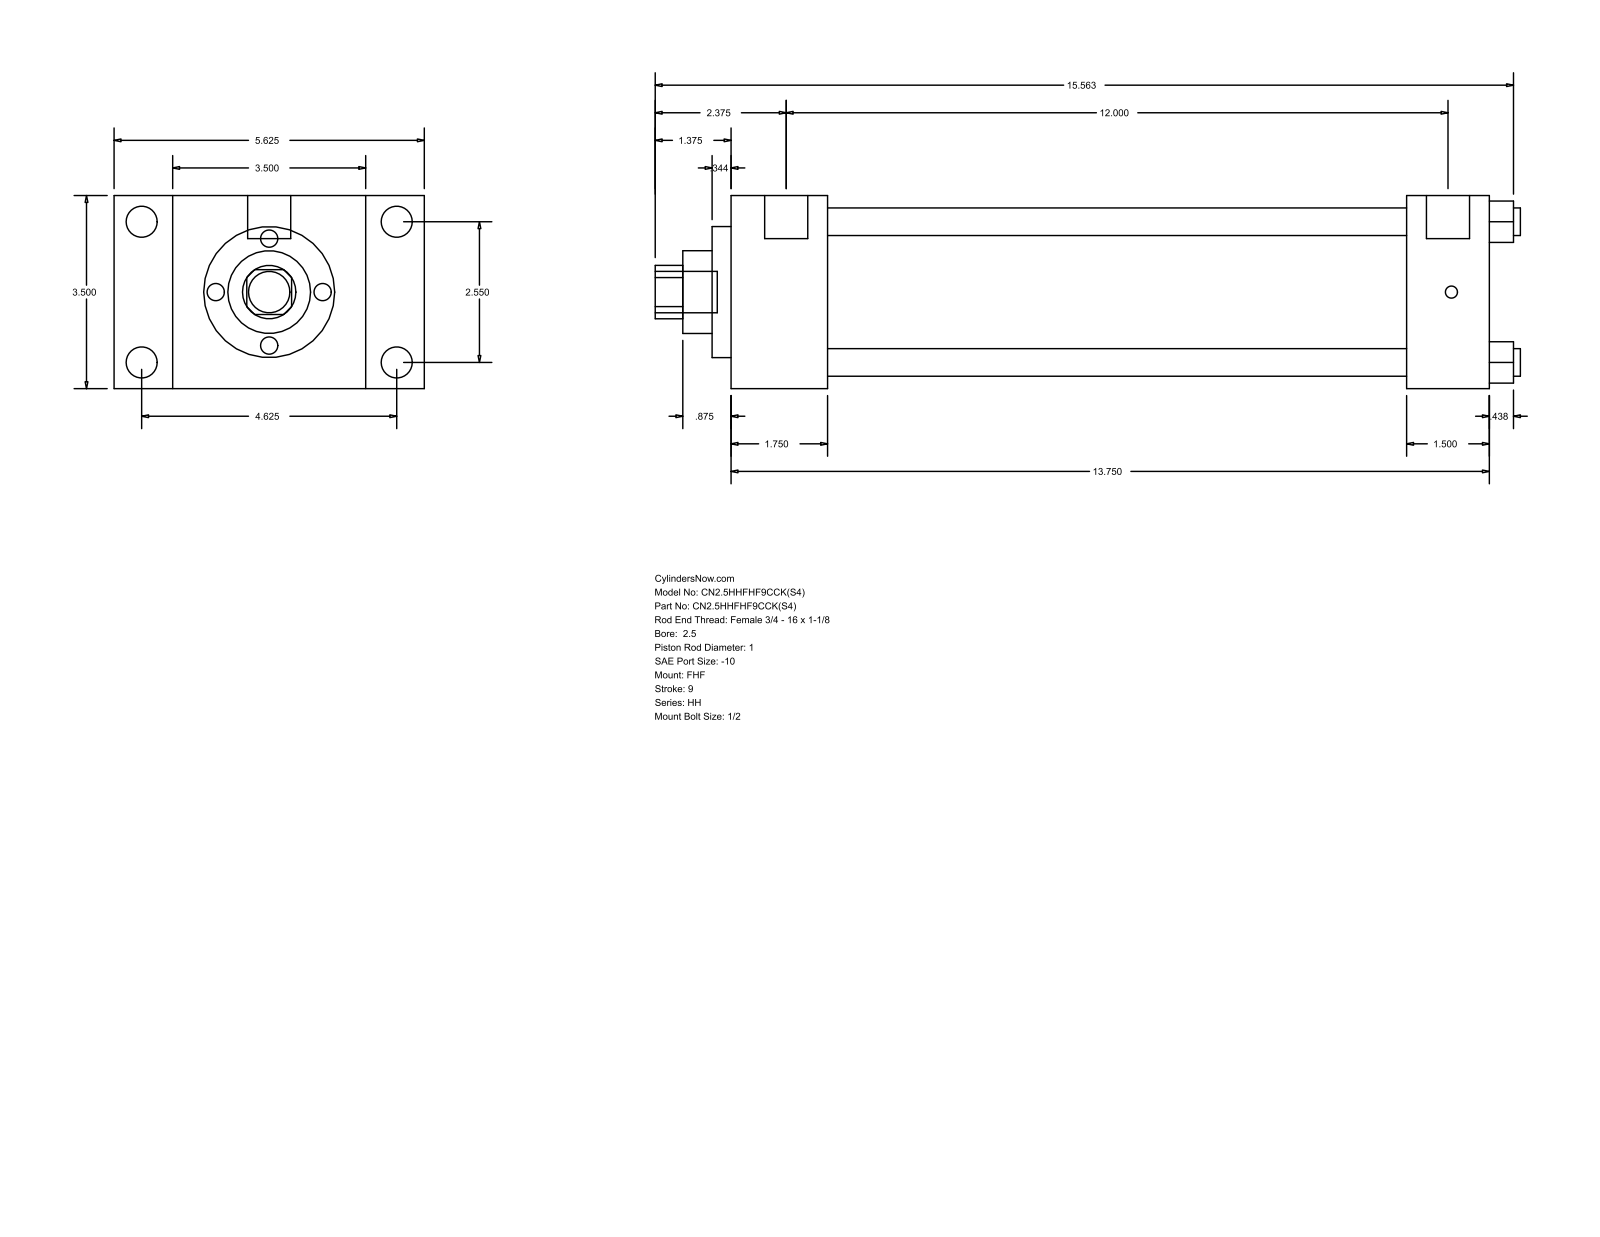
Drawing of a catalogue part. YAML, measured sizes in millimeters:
part_name: "HH_FHF__0250_1"
step_written_by: "GSSL Pune (CONFIG_CONTROL_DESIGN)"
units: millimeters
bodies: {solids: 0, faces: 90, planar: 61, cylindrical: 29, other: 0}
overall_size: [398.46, 142.88, 88.9]
round_holes:
  - {diameter: 12.7, count: 4}
  - {diameter: 25.4, count: 1}
  - {diameter: 38.1, count: 1}
  - {diameter: 60.33, count: 1}
  - {diameter: 73.03, count: 1}
round_bosses_or_shafts:
  - {diameter: 14.3, count: 4}
  - {diameter: 5.56, count: 4}
  - {diameter: 19.84, count: 2}
  - {diameter: 19.05, count: 1}
partial_cylinders:
  - {radius: 12.29, count: 1}
face_to_face_distances: [88.9, 44.46, 26.99, 115.89, 349.26, 304.8, 142.88, 311.15, 266.69, 38.11]
hole_center_spacings: [45.79, 64.76, 91.58]
